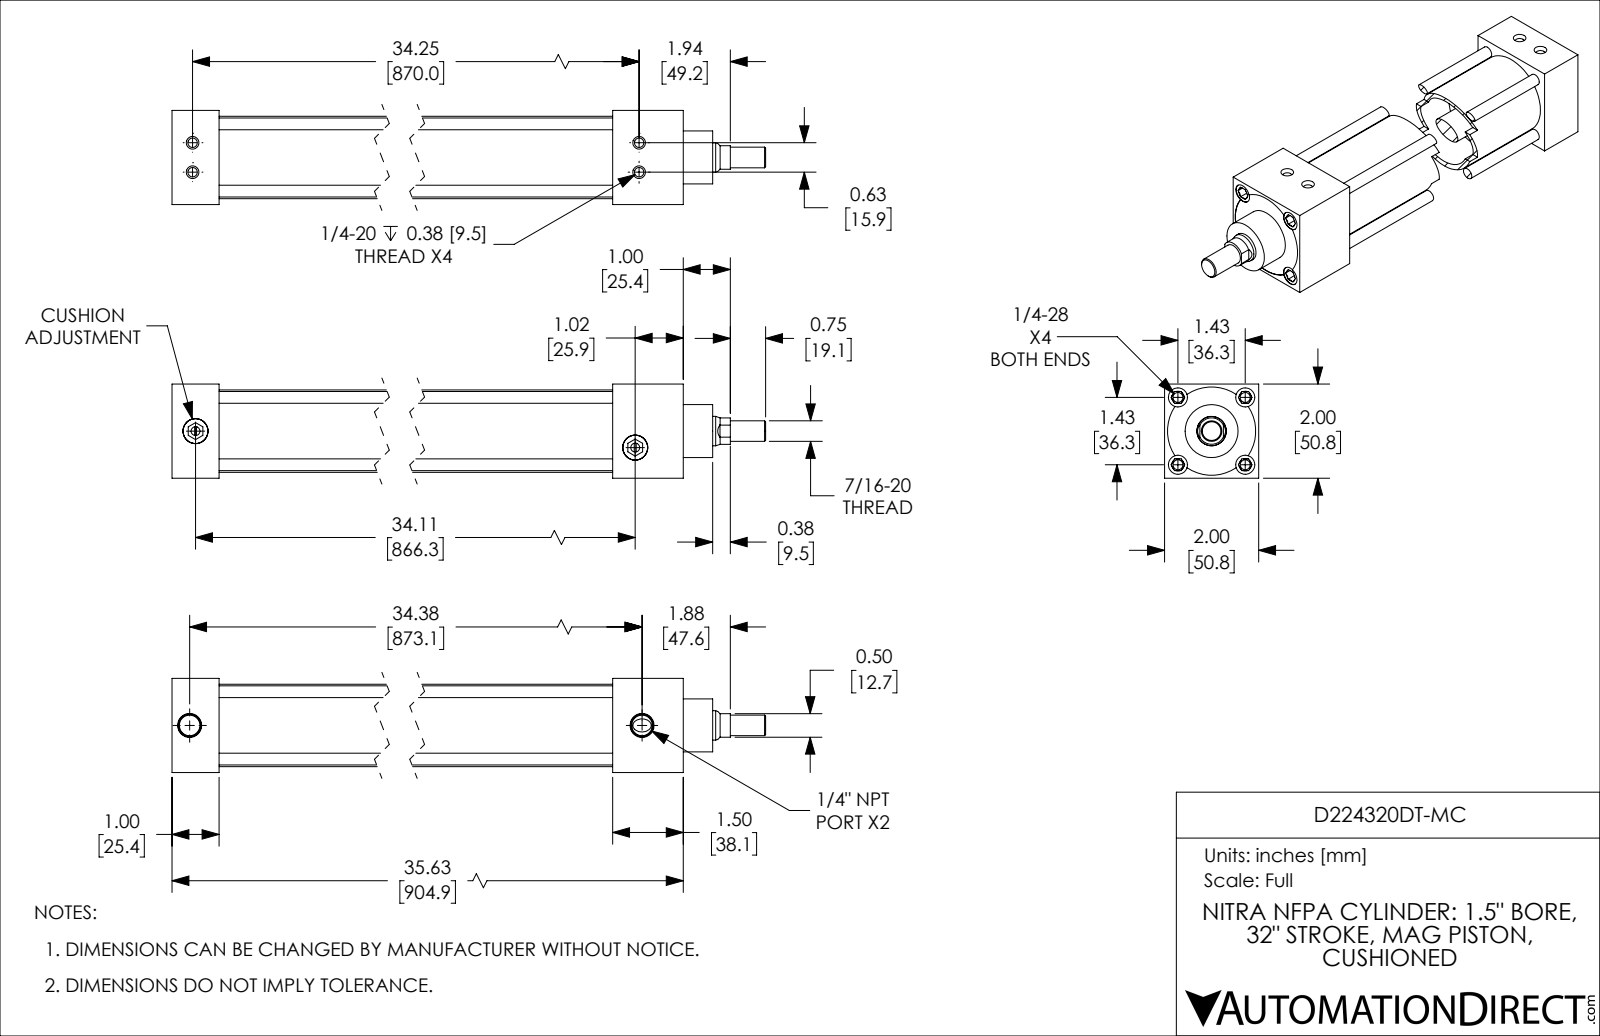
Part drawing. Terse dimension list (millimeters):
name: D224320DT-MC_PISTON_KK1; D224320DT-MC_BODY; D224320DT-MC_CUSHION; D224320DT-MC
written by: SolidWorks 2019 (CONFIG_CONTROL_DESIGN)
unit: mm
bodies: 4 solids, 251 faces (90 planar, 81 cylindrical, 80 other)
size: 949.3 × 50.8 × 50.8
volume: 814 100 mm³; area: 367 200 mm²
holes: 4× ⌀5.1, 4× ⌀5.4, 4× ⌀10.3, 2× ⌀4.8, 2× ⌀11.1, 2× ⌀13.5, 1× ⌀15.9, 1× ⌀38.1
bosses: 4× ⌀6.4, 2× ⌀13.5, 1× ⌀44.5, 1× ⌀38.1, 1× ⌀28.6, 1× ⌀15.8, 1× ⌀11.1
rounds: 1× R7.1, 1× R23.8
face distances: 50.8, 25.4, 866.8, 841.4, 904.7, 879.3, 38, 28.6, 54, 812.8
hole spacings: 8.1, 25.7, 36.3, 15.9, 51.4, 870, 870.1, 871.6
